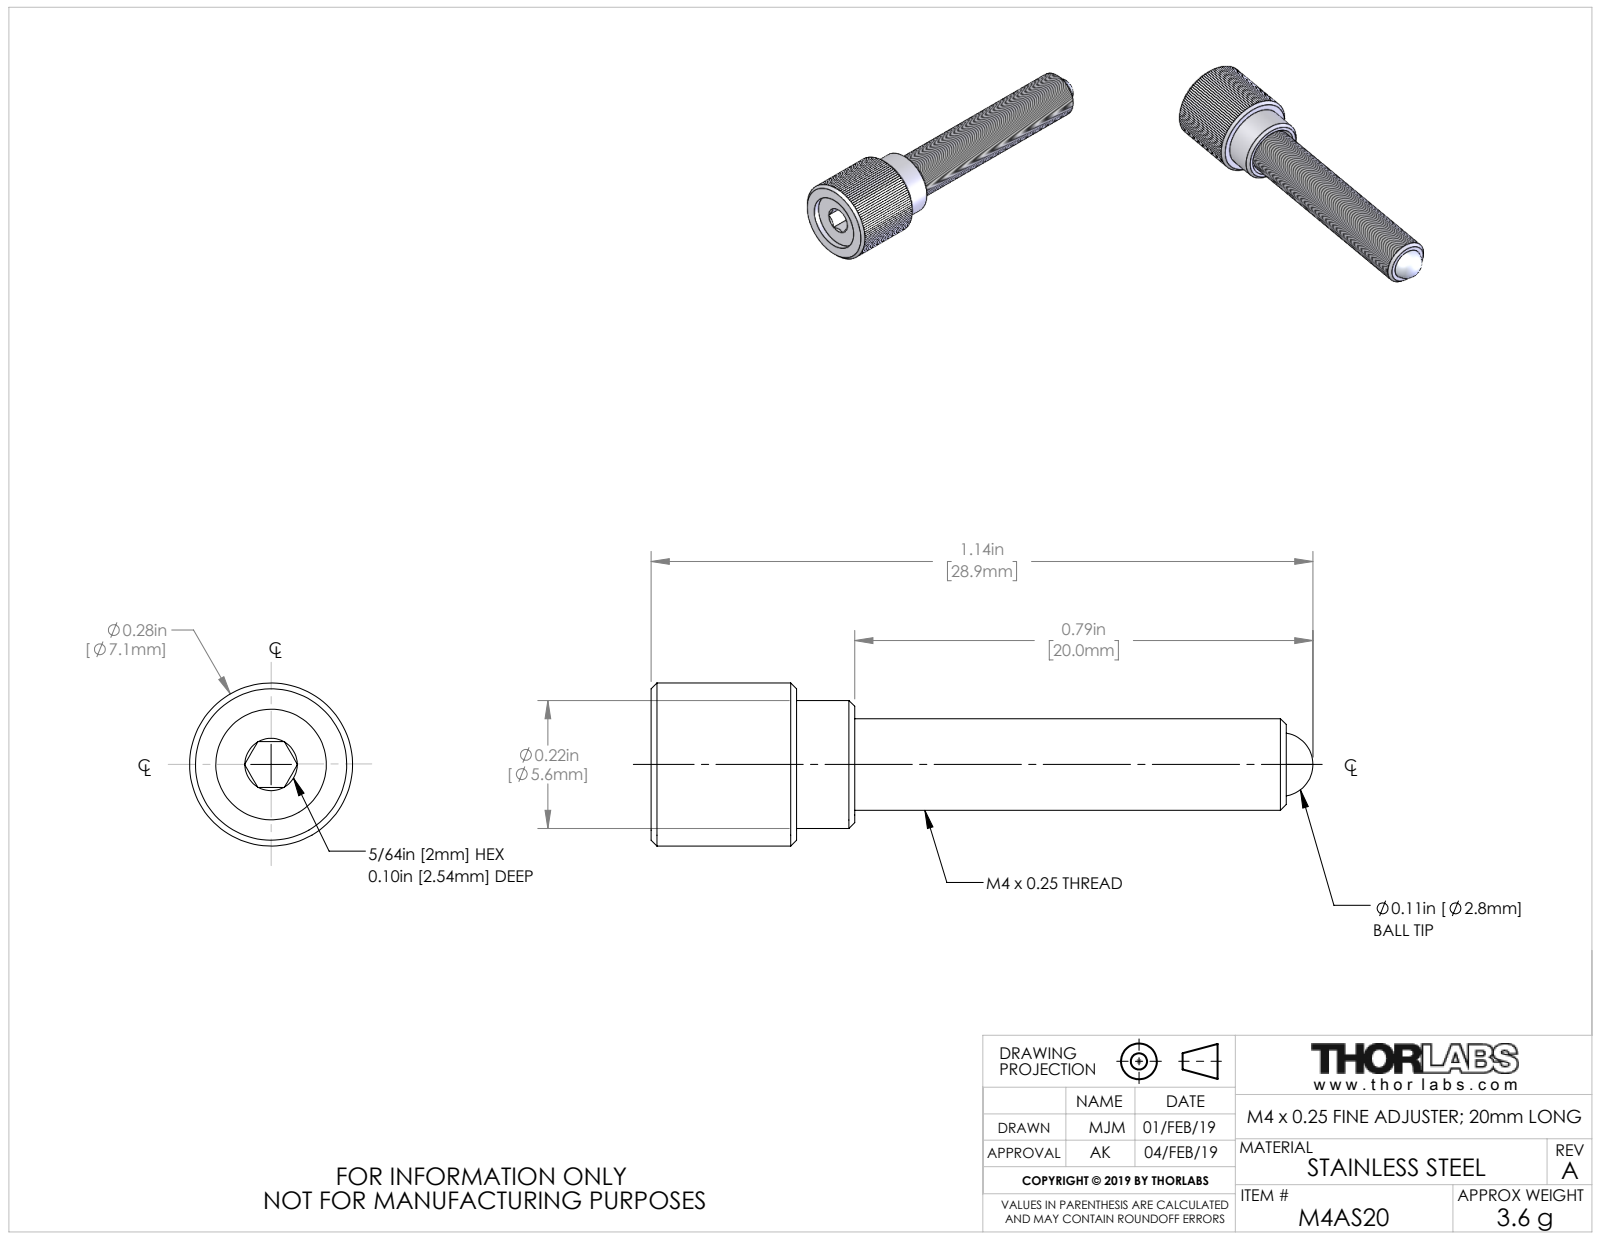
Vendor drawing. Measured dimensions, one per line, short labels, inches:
name: TTN175599-E0W
written by: SolidWorks 2018 (AUTOMOTIVE_DESIGN)
unit: in
bodies: 3 solids, 50 faces (14 planar, 12 cylindrical, 24 other)
size: 1.137 × 0.28 × 0.28
volume: 0.032 in³; area: 1.062 in²
holes: 1× ⌀0.11, 1× ⌀0.157, 1× ⌀0.19
bosses: 1× ⌀0.28, 1× ⌀0.22, 1× ⌀0.157
face distances: 0.1, 0.13, 0.02, 0.23, 0.15, 0.25, 0.057, 0.043, 0.172, 0.193
